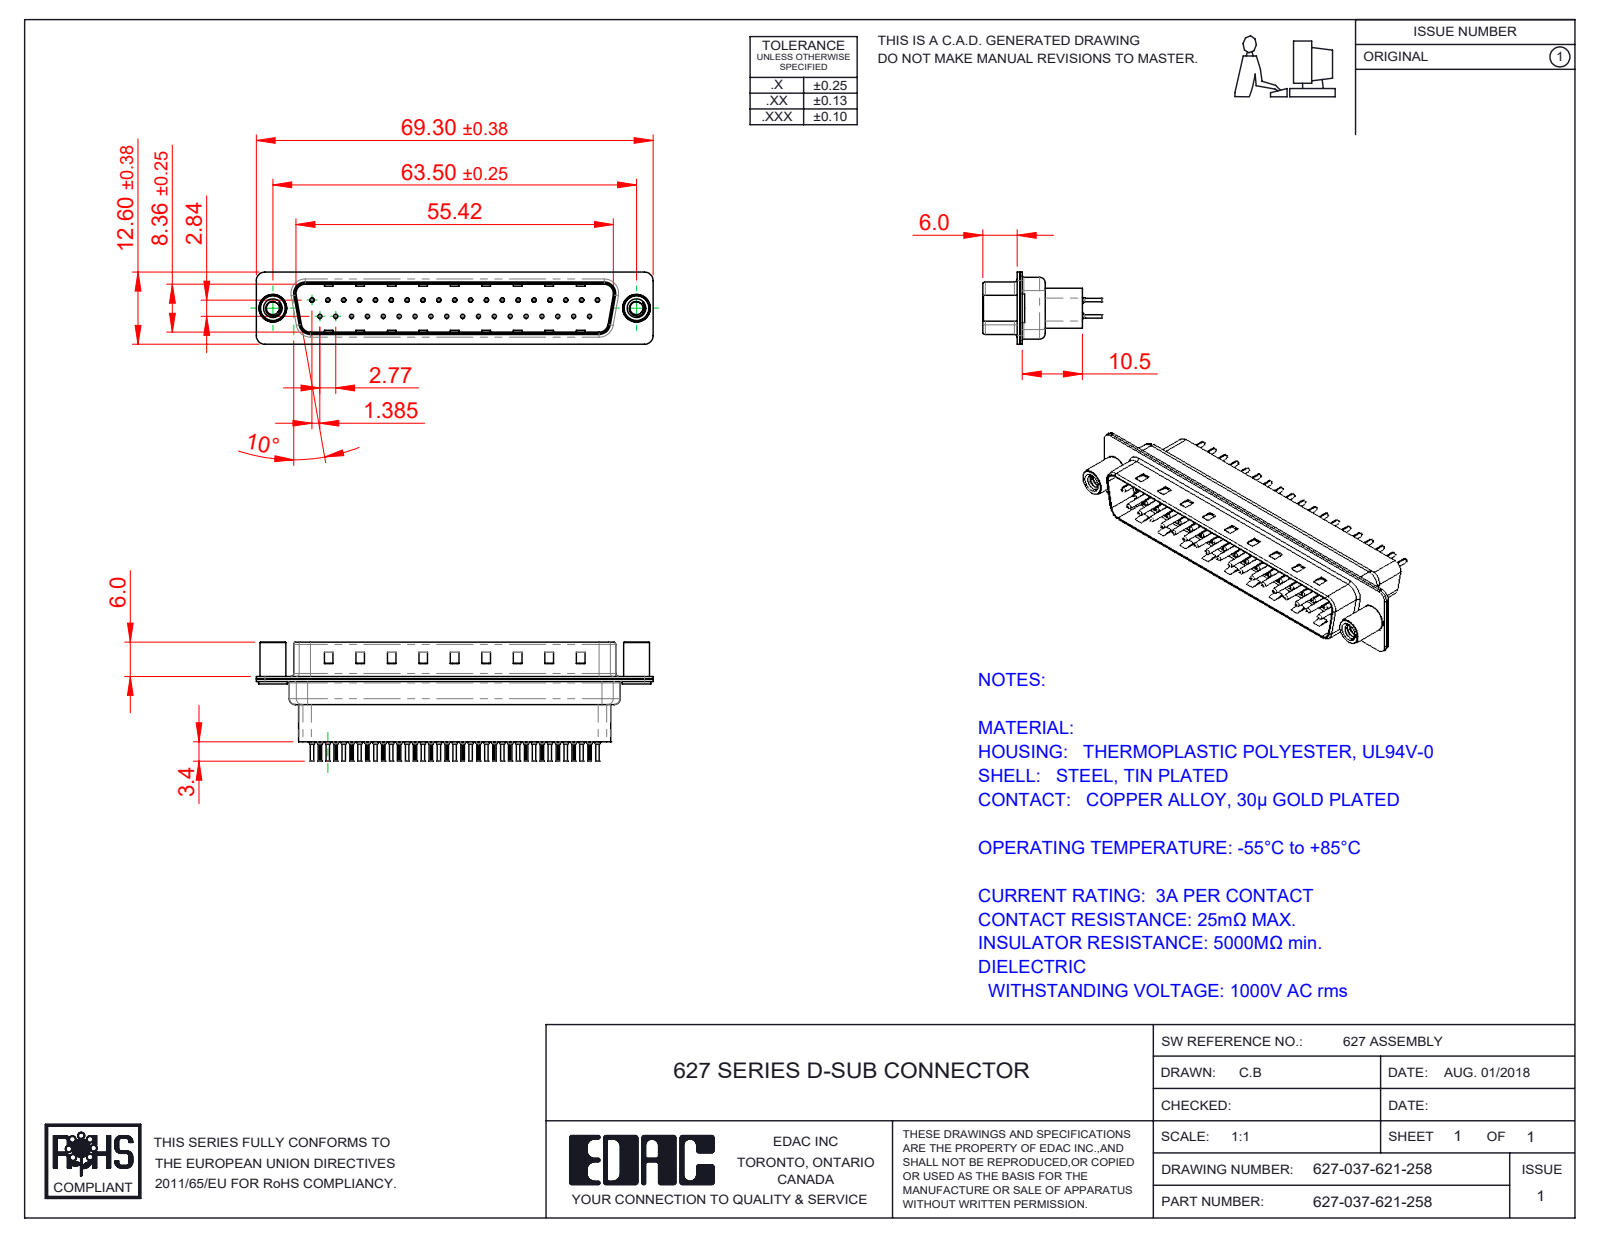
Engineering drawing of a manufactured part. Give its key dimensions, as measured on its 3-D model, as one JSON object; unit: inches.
{"part_name": "627 Contact Row 1_21H; 627 Contact Row 2_21H; 627-037-621-058; 627 4-40 Threaded Standoff (+3 more)", "step_written_by": "SolidWorks 2020 (CONFIG_CONTROL_DESIGN)", "units": "inches", "bodies": {"solids": 42, "faces": 4072, "planar": 1093, "cylindrical": 1538, "other": 1441}, "overall_size": [2.728, 0.819, 0.496], "volume_in3": 0.328, "surface_area_in2": 21.32, "round_holes": [[0.008, 37], [0.014, 37], [0.043, 37], [0.063, 37], [0.089, 2], [0.157, 2], [0.189, 2]], "round_bosses_or_shafts": [[0.079, 37], [0.059, 37], [0.03, 37], [0.024, 37], [0.197, 2], [0.193, 2], [0.177, 2]], "partial_cylinders_radius": [[0.004, 74], [0.059, 16], [0.079, 12], [0.02, 8], [0.063, 8], [0.01, 4], [0.024, 4], [0.026, 4]], "face_to_face_distances": [0.016, 0.032, 0.377, 0.027, 0.302, 0.018, 0.059, 0.043, 0.318, 0.345], "hole_center_spacings": [0.124, 0.109, 0.218, 0.327, 0.198, 0.398, 0.436, 0.503]}
